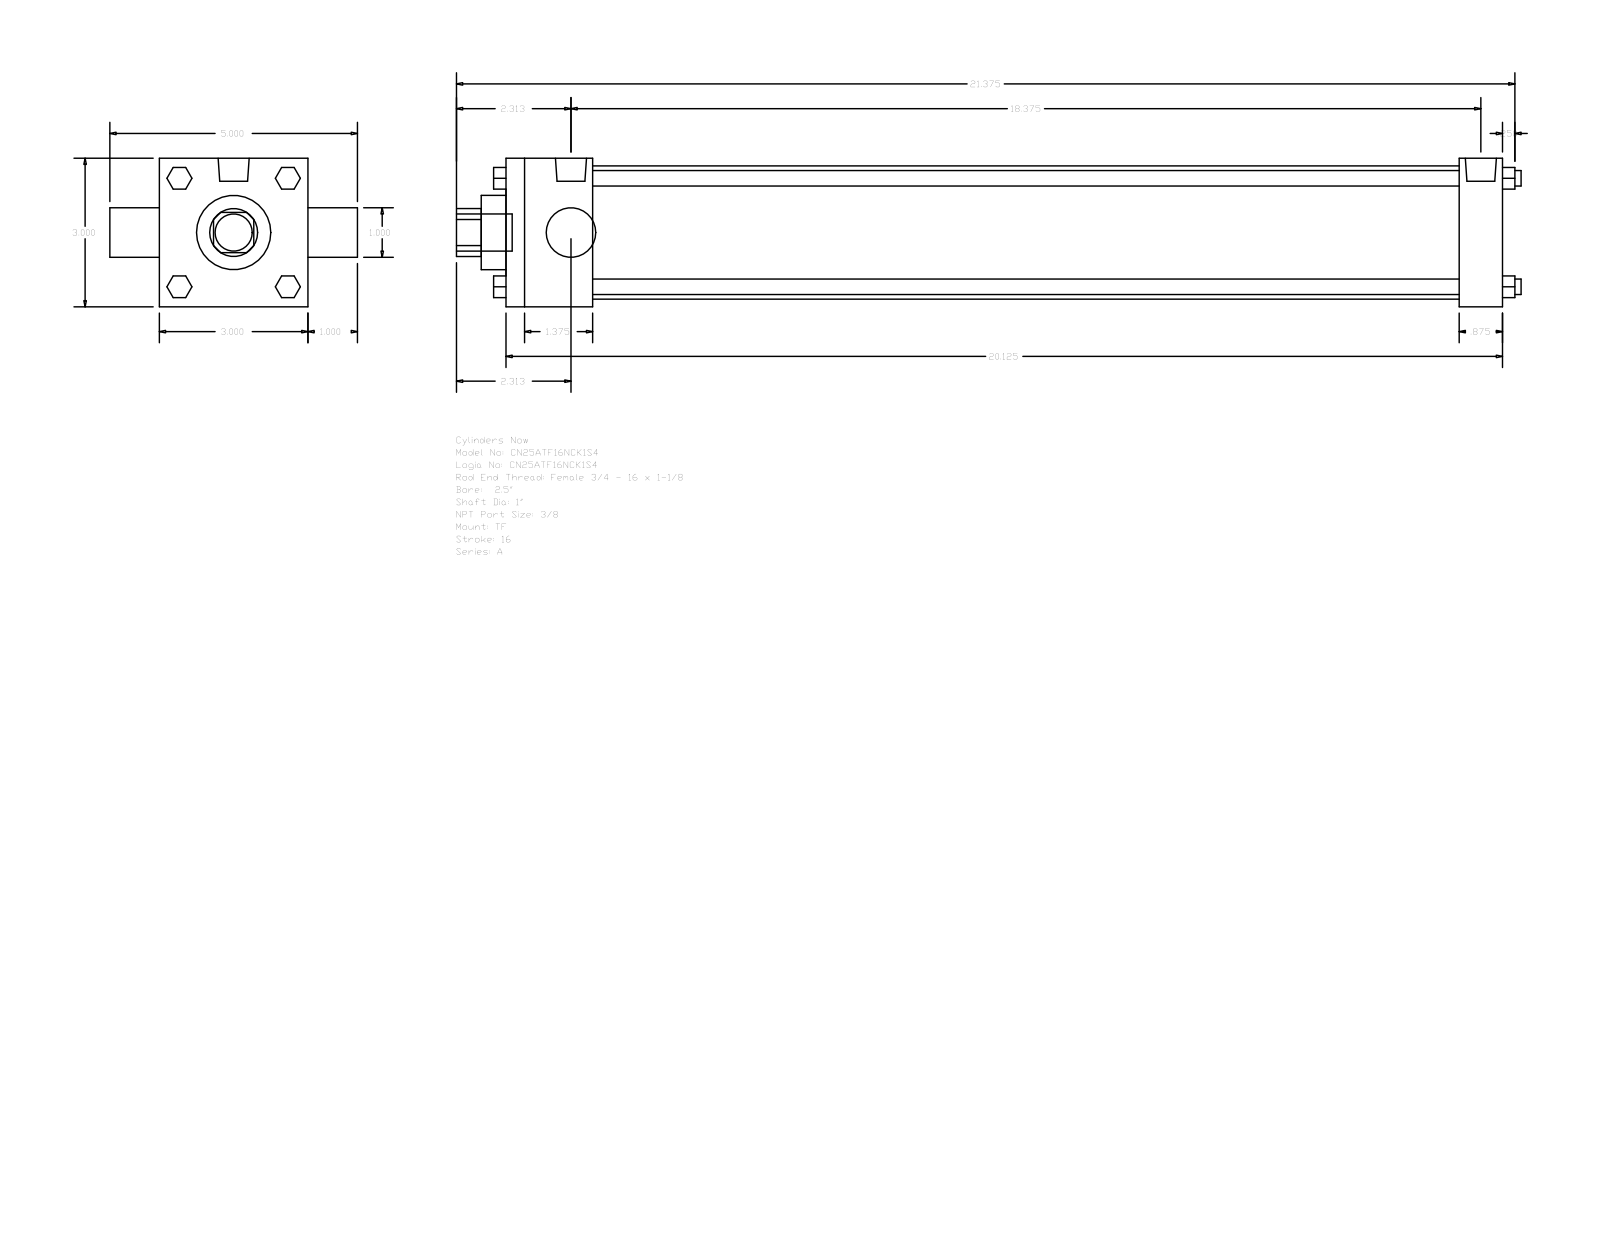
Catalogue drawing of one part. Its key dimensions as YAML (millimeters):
part_name: "A_TF__0250_1"
step_written_by: "GSSL Pune (CONFIG_CONTROL_DESIGN)"
units: millimeters
bodies: {solids: 0, faces: 120, planar: 92, cylindrical: 28, other: 0}
overall_size: [546.1, 127, 76.2]
round_holes:
  - {diameter: 25.4, count: 2}
  - {diameter: 38.1, count: 1}
  - {diameter: 68.33, count: 1}
round_bosses_or_shafts:
  - {diameter: 7.94, count: 4}
  - {diameter: 5.56, count: 3}
  - {diameter: 15.93, count: 2}
  - {diameter: 19.05, count: 1}
partial_cylinders:
  - {radius: 12.29, count: 1}
face_to_face_distances: [76.2, 511.18, 44.45, 488.95, 444.5, 466.73, 22.23, 25.4, 101.6, 12.7]
